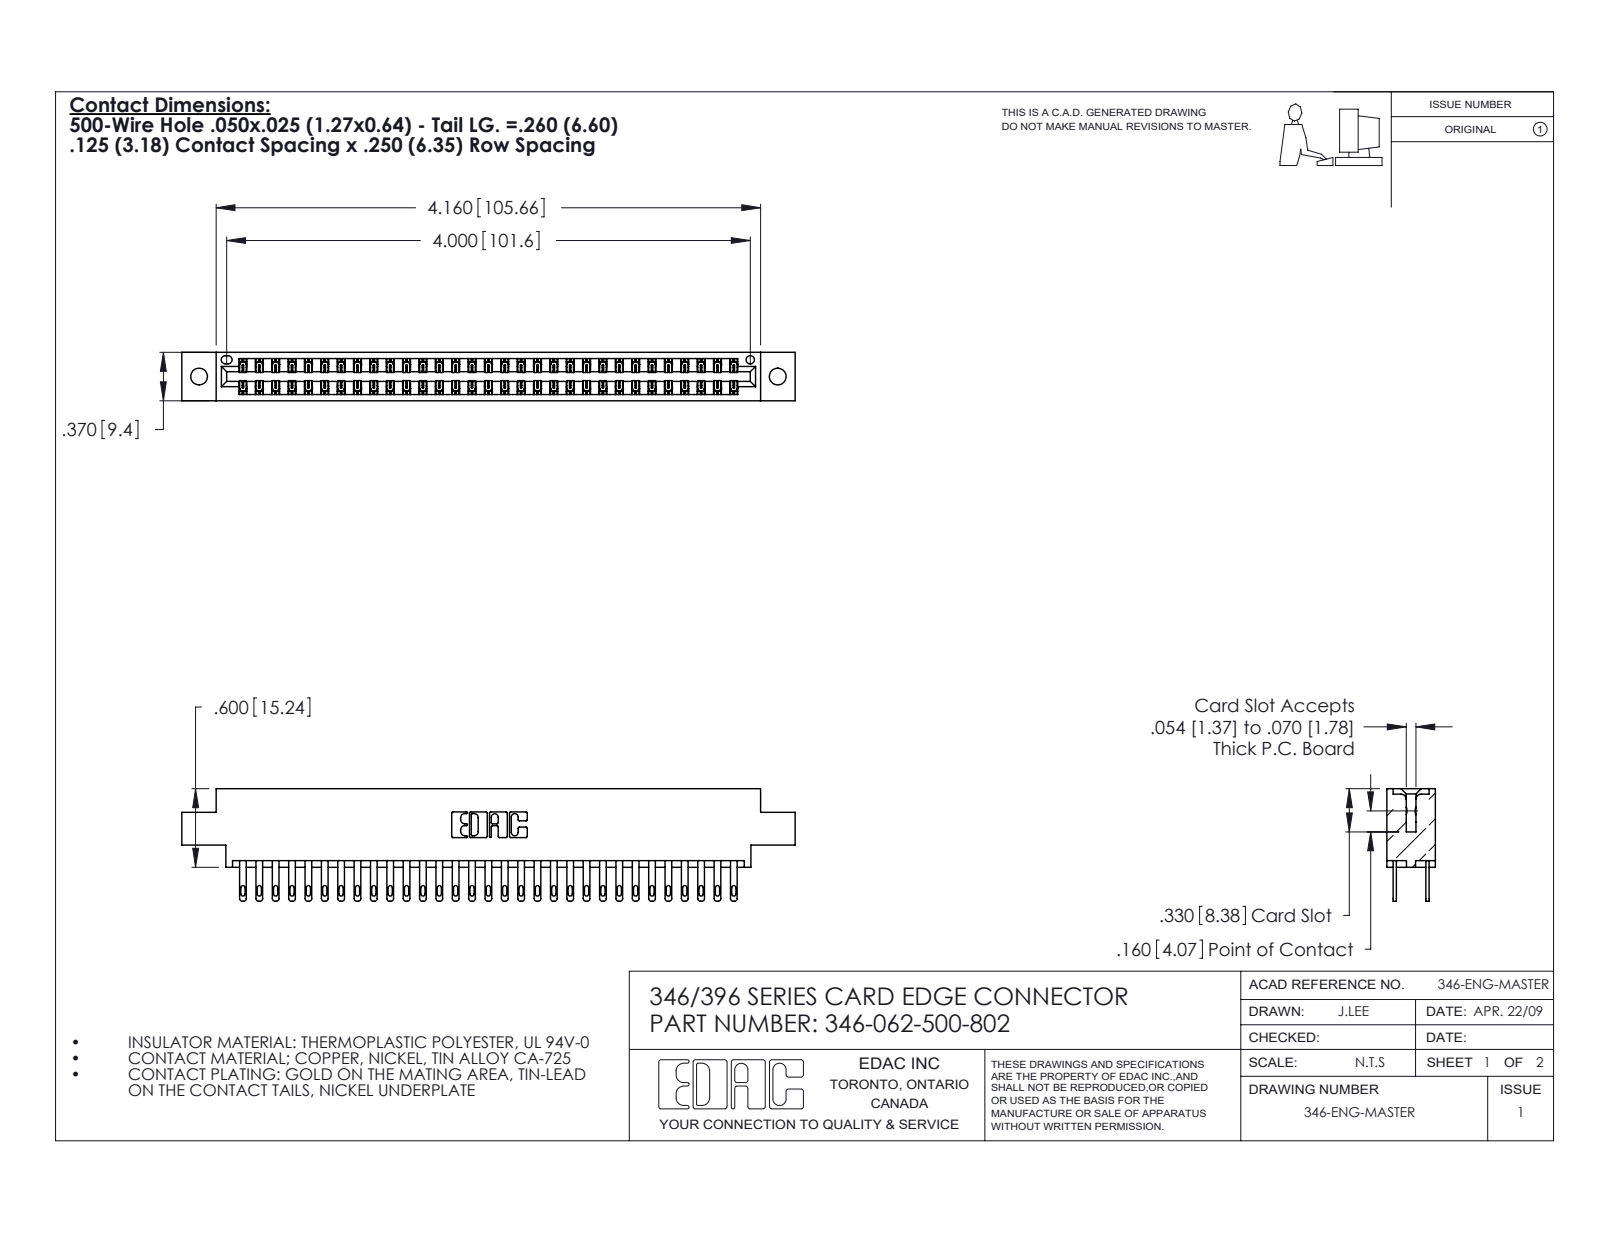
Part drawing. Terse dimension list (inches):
name: 346-062-500-802; 345-292-001_345-293-100; 346 Part_0.170 Offset - 0.128 Dia
written by: SolidWorks 2020 (CONFIG_CONTROL_DESIGN)
unit: in
bodies: 63 solids, 3102 faces (1878 planar, 1224 cylindrical, 0 other)
size: 4.685 × 0.86 × 0.37
volume: 0.703 in³; area: 25.14 in²
holes: 2× ⌀0.128, 1× ⌀0.064
rounds: 93× R0.006, 62× R0.016, 62× R0.02, 22× R0.01, 6× R0.007, 6× R0.031, 3× R0.026, 2× R0.014
face distances: 0.048, 0.322, 0.25, 0.37, 0.072, 0.298, 0.025, 0.275, 0.148, 0.222
hole spacings: 0.246, 4.212, 4.42
